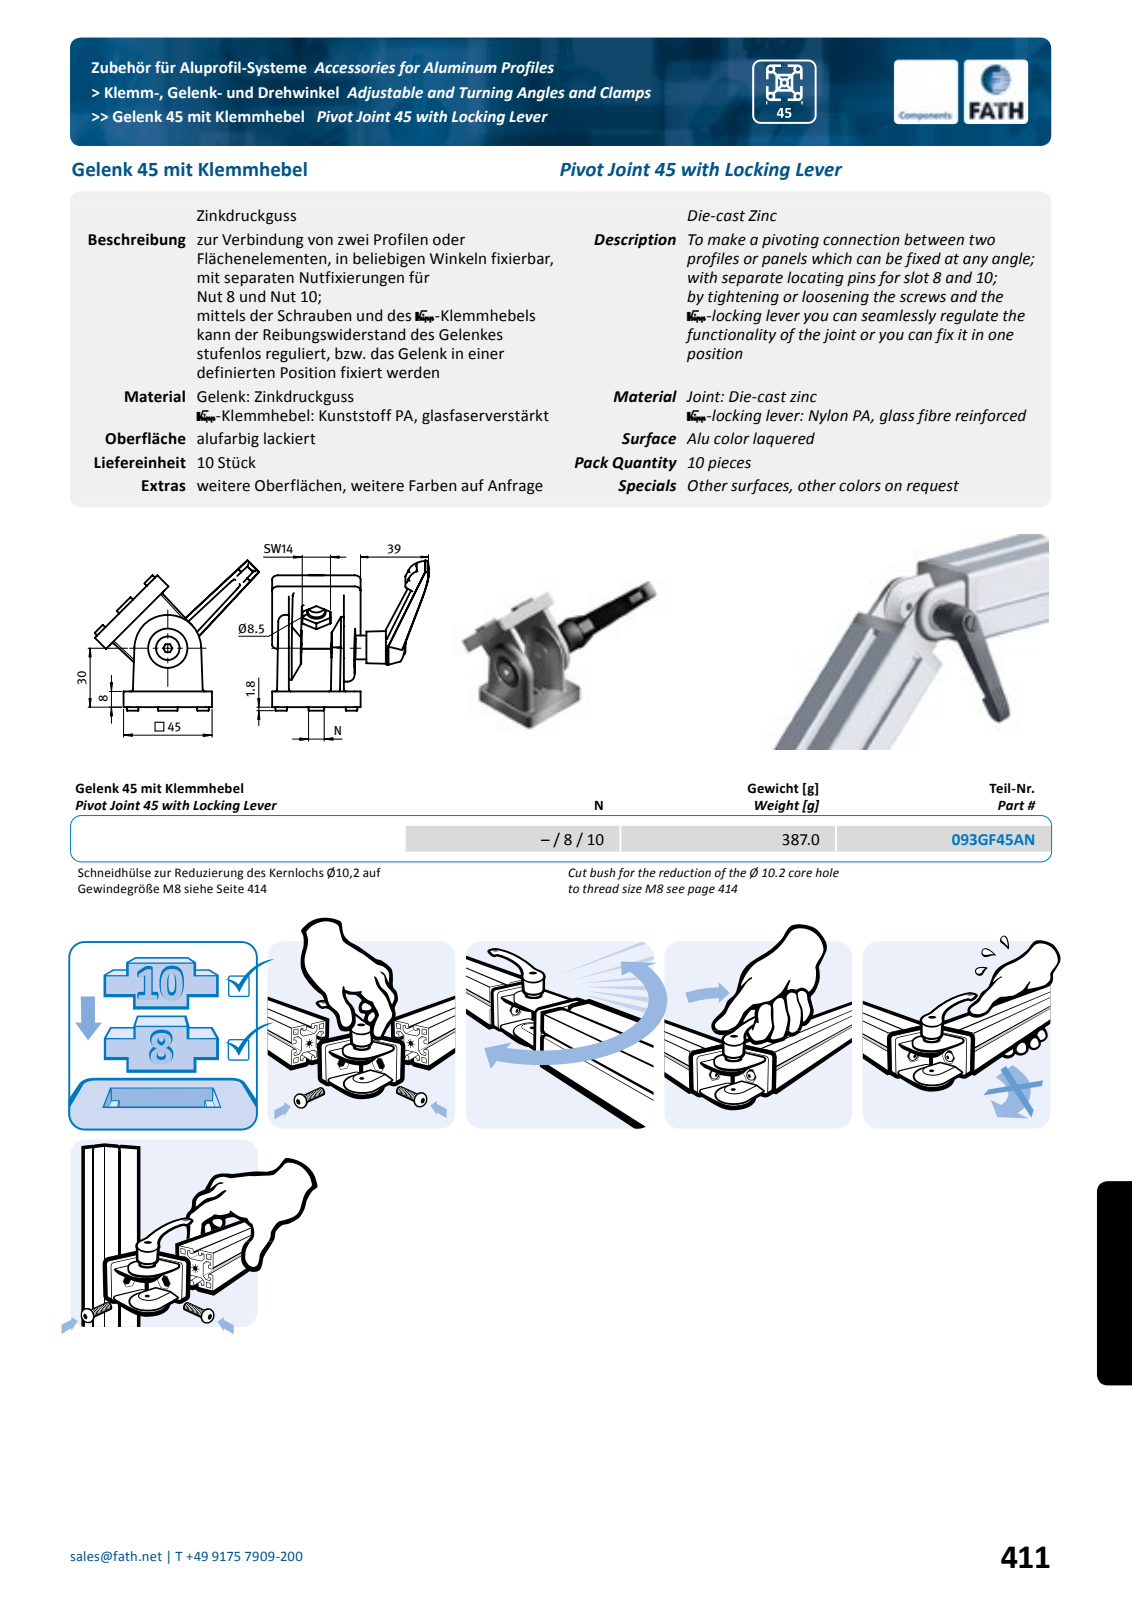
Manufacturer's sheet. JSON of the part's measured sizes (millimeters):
{"part_name": "fath_093gf45an_1; fath_093gf45an_2; fath_093gf45an_3; fath_093gf45an_4 (+8 more)", "step_written_by": "Spatial InterOp 3D (automotive_design)", "units": "millimeters", "bodies": {"solids": 13, "faces": 1567, "planar": 298, "cylindrical": 505, "other": 764}, "overall_size": [83.06, 78.93, 71.43], "volume_mm3": 61242, "surface_area_mm2": 38265, "round_holes": [[2, 4], [5, 1], [5.6, 1], [6.4, 1], [10.6, 1], [12.2, 1], [13, 1], [14, 1], [16.2, 1], [24, 1], [26, 1]], "round_bosses_or_shafts": [[34, 1], [32, 1], [25.8, 1], [23.6, 1], [16, 1], [13.5, 1], [12, 1], [10, 1]], "partial_cylinders_radius": [[0.3, 156], [0.2, 53], [1, 20], [0.5, 15], [1.5, 8], [3, 8], [0.97, 4], [3.5, 4]], "face_to_face_distances": [8, 35.8, 28, 1, 0.7, 27.3, 8.5, 9.2, 36.5, 5.57], "hole_center_spacings": [8.03, 10.49, 10.5, 19.4, 20.99, 21]}
